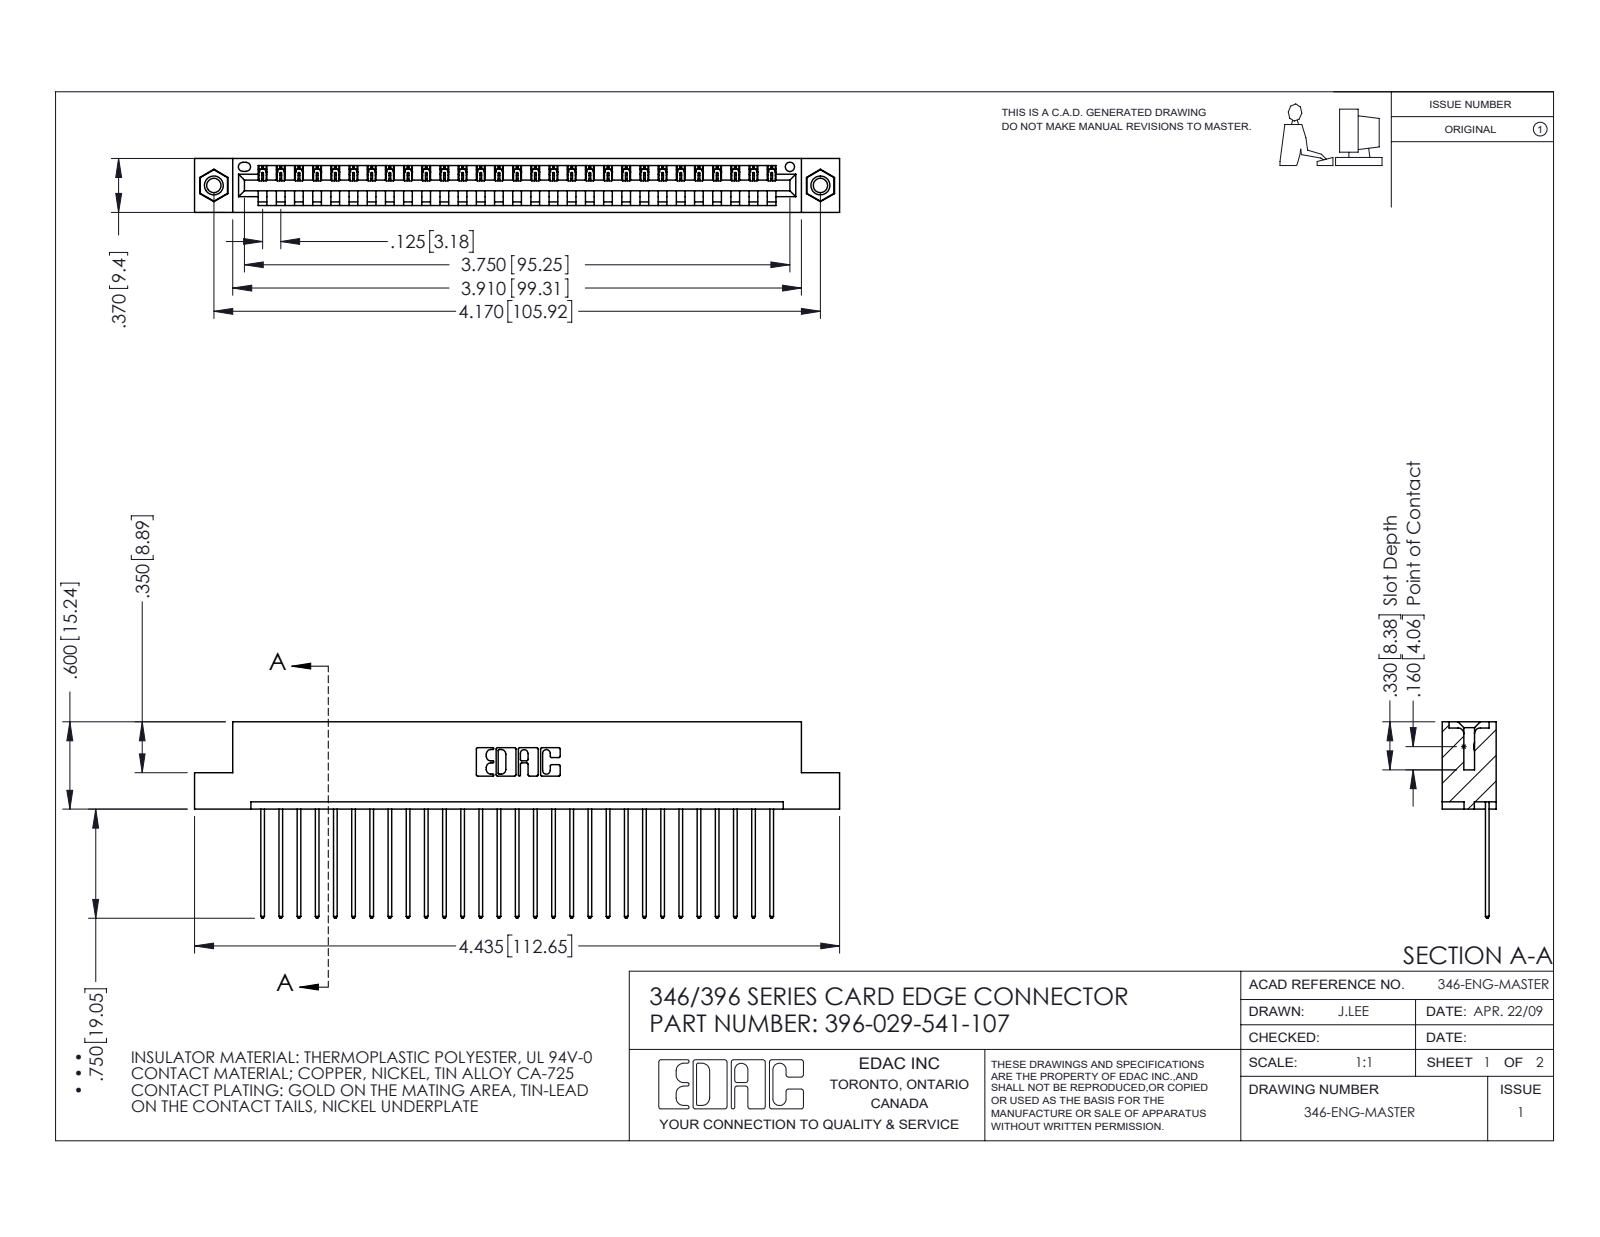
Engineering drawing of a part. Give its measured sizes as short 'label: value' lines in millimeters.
name: 346 Part_Flush Mounting Lugs - 0.156 Dia-TI; 345-292-001_345-293-141; 345-250-001_345-250-005-103; 396-029-541-107
written by: SolidWorks 2016 (CONFIG_CONTROL_DESIGN)
unit: mm
bodies: 32 solids, 1864 faces (1268 planar, 580 cylindrical, 16 other)
size: 112.6 × 34.3 × 9.4
volume: 10 800 mm³; area: 13 940 mm²
holes: 2× ⌀2.5, 2× ⌀3.2, 2× ⌀4, 1× ⌀1.6
bosses: 2× ⌀3.9
rounds: 58× R0.2, 58× R0.3, 22× R0.3, 6× R0.2, 6× R0.8, 3× R0.7, 2× R0.8, 2× R1
face distances: 1.2, 8.2, 9.4, 6.4, 1.8, 7.6, 0.6, 3.8, 5.6, 2.5
hole spacings: 6.2, 100.6, 105.9
